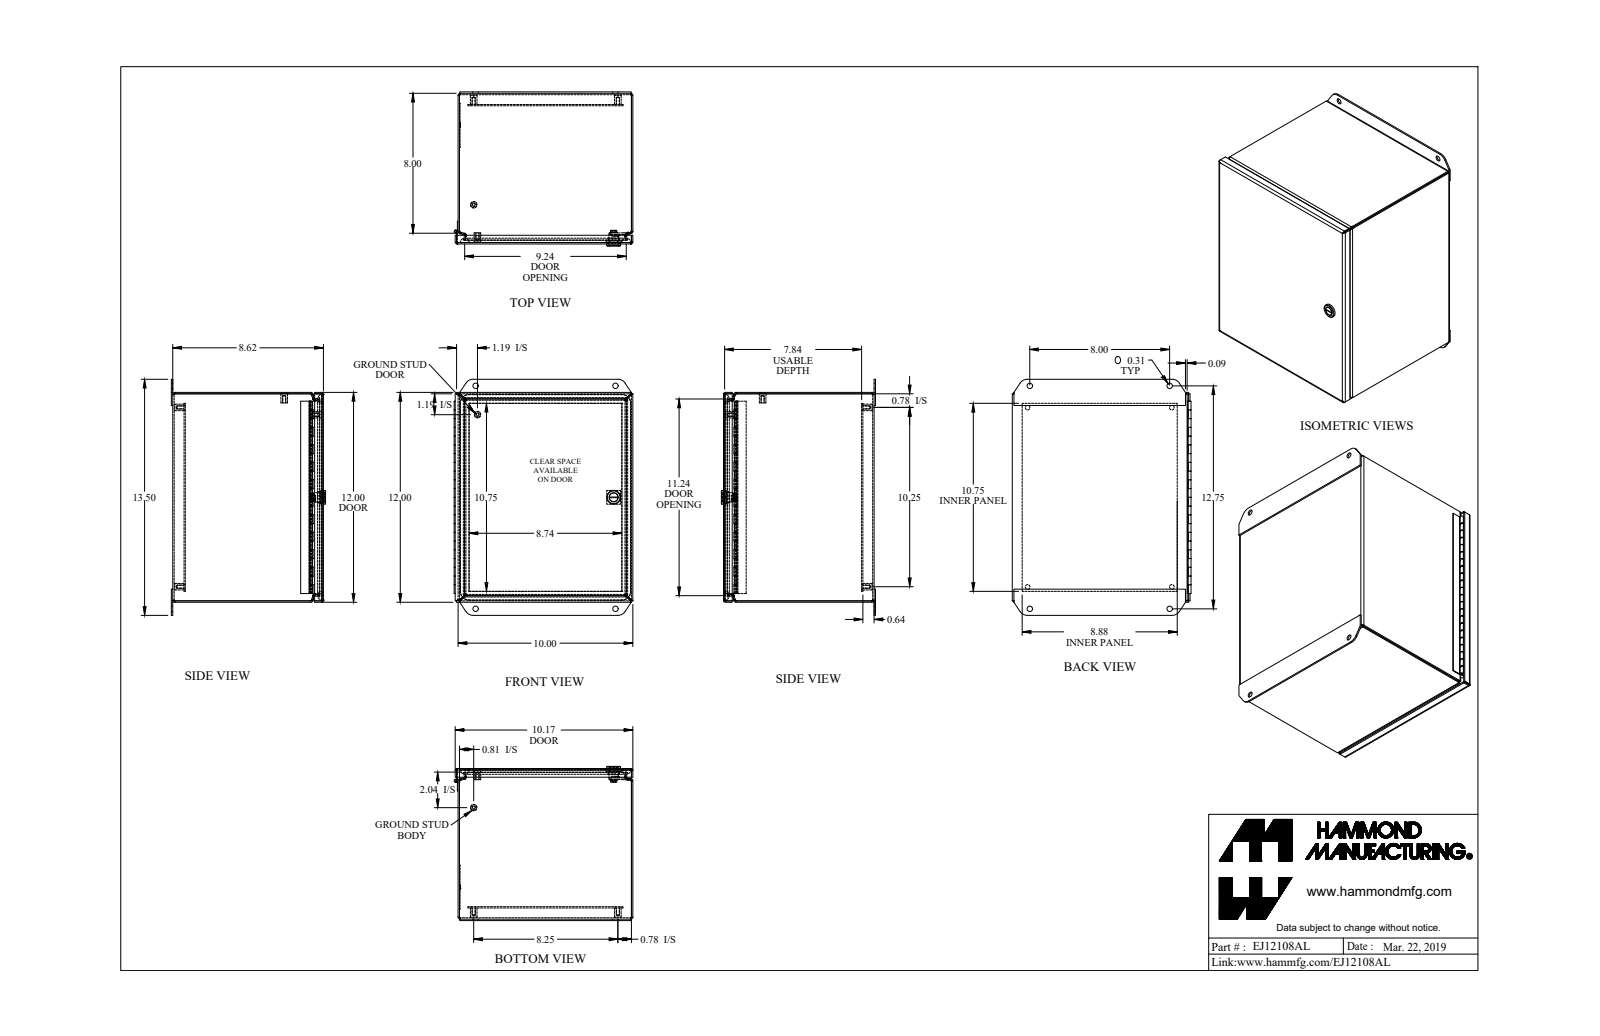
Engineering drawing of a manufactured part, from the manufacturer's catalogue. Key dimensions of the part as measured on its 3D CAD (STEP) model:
Part name (STEP PRODUCT): EJ12108AL_Default
STEP written by: SolidWorks 2019 (CONFIG_CONTROL_DESIGN)
Units: inches
Bodies: 14 solids, 658 faces (432 planar, 158 cylindrical, 68 other)
Overall size (bounding box): 13.5 × 10.226 × 8.82
Volume: 65.22 in³ · Surface area: 1 658 in²
Round holes (diameter × count): ⌀0.159 ×6, ⌀0.265 ×4, ⌀0.313 ×4, ⌀0.516 ×1
Round bosses / shafts (diameter × count): ⌀0.375 ×6, ⌀0.33 ×6, ⌀0.788 ×1, ⌀0.535 ×1, ⌀0.496 ×1, ⌀0.435 ×1, ⌀0.18 ×1, ⌀0.1 ×1
Partial cylindrical surfaces — rounded edges, fillets, slot ends (radius × count): R0.041 ×16, R0.121 ×16, R0.281 ×12, R0.25 ×4, R0.499 ×4, R0.5 ×4, R0.06 ×2, R0.03 ×1
Main face-to-face distances: 0.081, 8.536, 9.919, 11.919, 8.617, 8.455, 10, 0.643, 7.974, 0.562
Hole centre spacings: 1.256, 8.22, 11.501, 13.158, 14.081, 0.024, 5.13, 6.376
